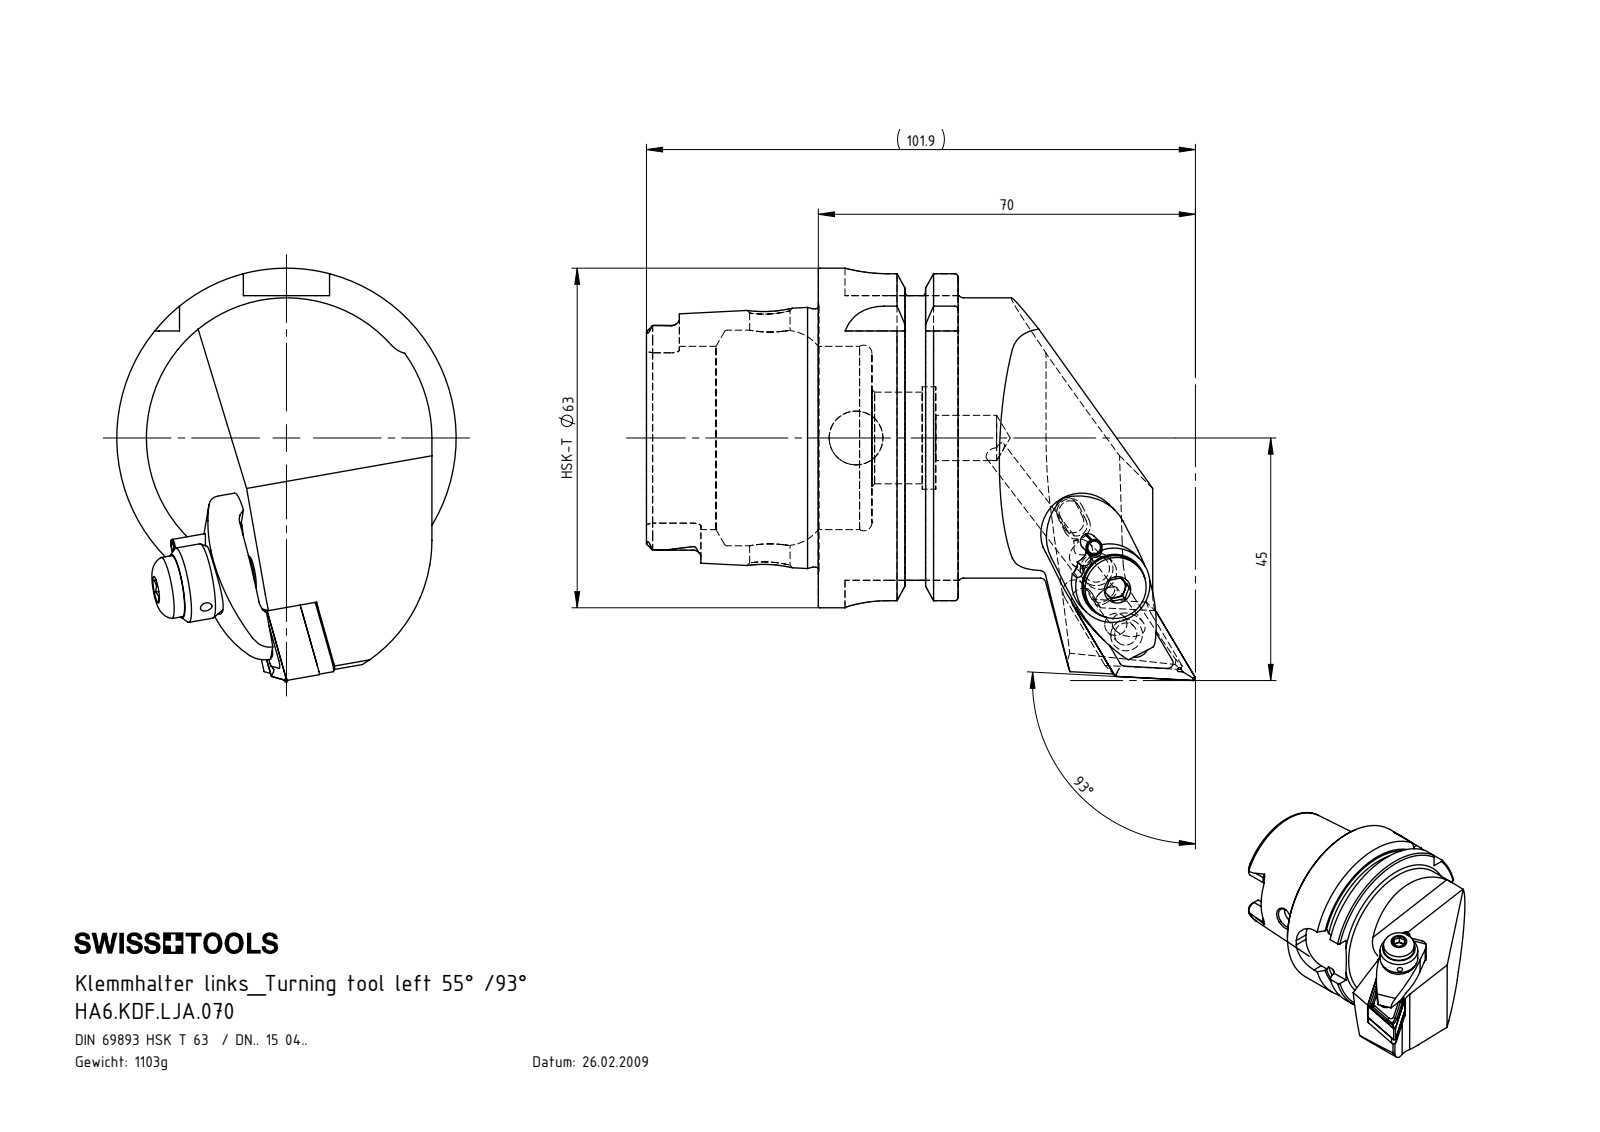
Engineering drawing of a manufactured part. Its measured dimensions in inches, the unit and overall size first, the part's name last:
Units: inches
Overall size (bounding box): 4.012 × 3.012 × 2.48
Round holes (diameter × count): ⌀0.079 ×3, ⌀0.165 ×2, ⌀0.197 ×2, ⌀0.276 ×2, ⌀0.118 ×1, ⌀0.157 ×1, ⌀0.203 ×1, ⌀0.244 ×1, ⌀0.252 ×1, ⌀0.295 ×1, ⌀0.331 ×1, ⌀0.335 ×1
Round bosses / shafts (diameter × count): ⌀0.197 ×2, ⌀2.48 ×1, ⌀2.163 ×1, ⌀2.047 ×1, ⌀1.887 ×1, ⌀0.551 ×1, ⌀0.453 ×1, ⌀0.276 ×1
Partial cylindrical surfaces — rounded edges, fillets, slot ends (radius × count): R0.015 ×6, R0.027 ×6, R0.055 ×6, R0.016 ×4, R0.039 ×4, R0.315 ×4, R0.059 ×3, R0.079 ×2
Main face-to-face distances: 1.022, 0.63, 0.392, 1.256, 1.648, 2.278, 0.238, 2.079, 0.125, 0.363
Hole centre spacings: 0.315, 0.583, 0.59, 0.591, 0.906, 0.323
Volume: 8.631 in³ · Surface area: 53.72 in²
Bodies: 10 solids, 457 faces (123 planar, 149 cylindrical, 185 other)
Part name (STEP PRODUCT): HA6.KDF.LJA.070; KVT_MB_600_050; WCC-ER4.103.032_A; WCC-ER5.102.012_B (+6 more)
STEP written by: SolidWorks 2012 (AUTOMOTIVE_DESIGN)
